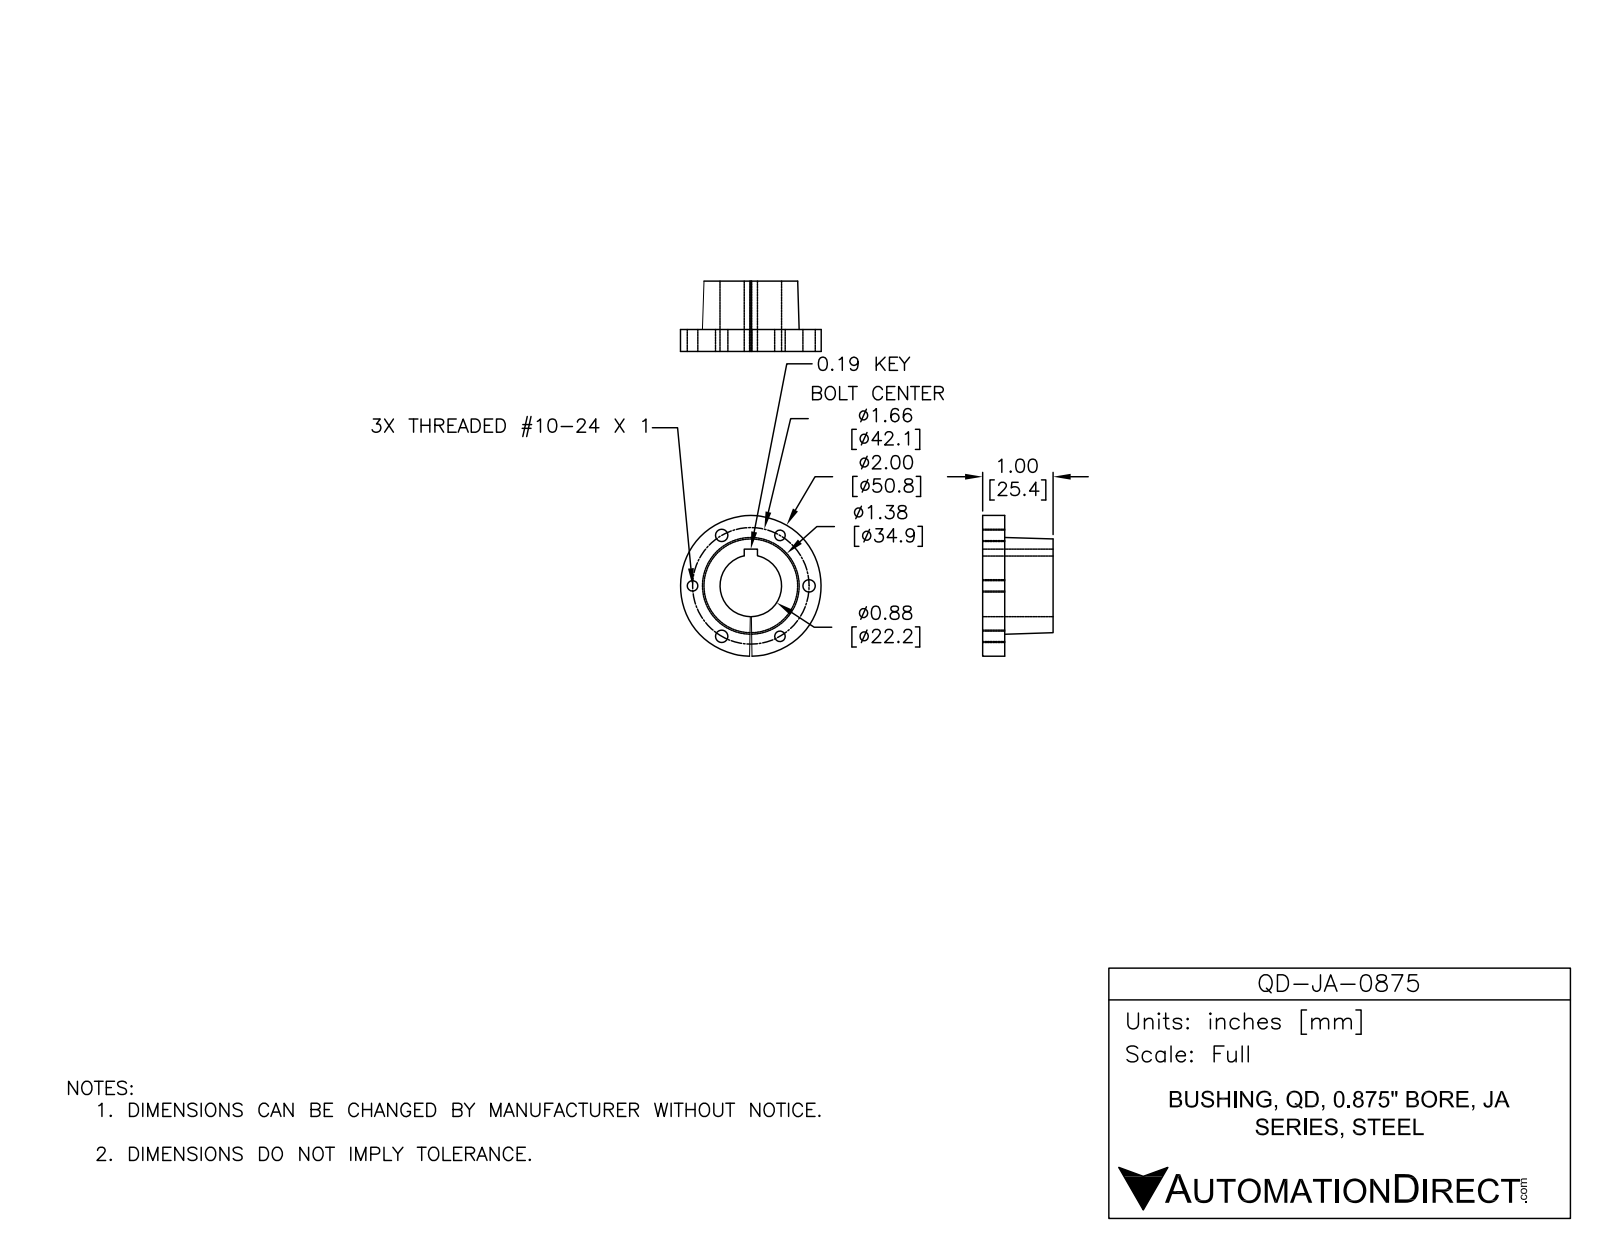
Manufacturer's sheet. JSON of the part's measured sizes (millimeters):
{"part_name": "QD-JA-0875", "step_written_by": "SolidWorks 2014 (AUTOMOTIVE_DESIGN)", "units": "millimeters", "bodies": {"solids": 1, "faces": 29, "planar": 8, "cylindrical": 18, "other": 3}, "overall_size": [50.8, 50.8, 25.4], "volume_mm3": 21390, "surface_area_mm2": 9103, "round_holes": [[3.8, 3], [4.4, 3], [22.2, 1]], "round_bosses_or_shafts": [[50.8, 1]], "face_to_face_distances": [8, 25.4, 17.4, 4.7], "hole_center_spacings": [21, 21, 36.4, 36.4, 42.1, 42.1]}
